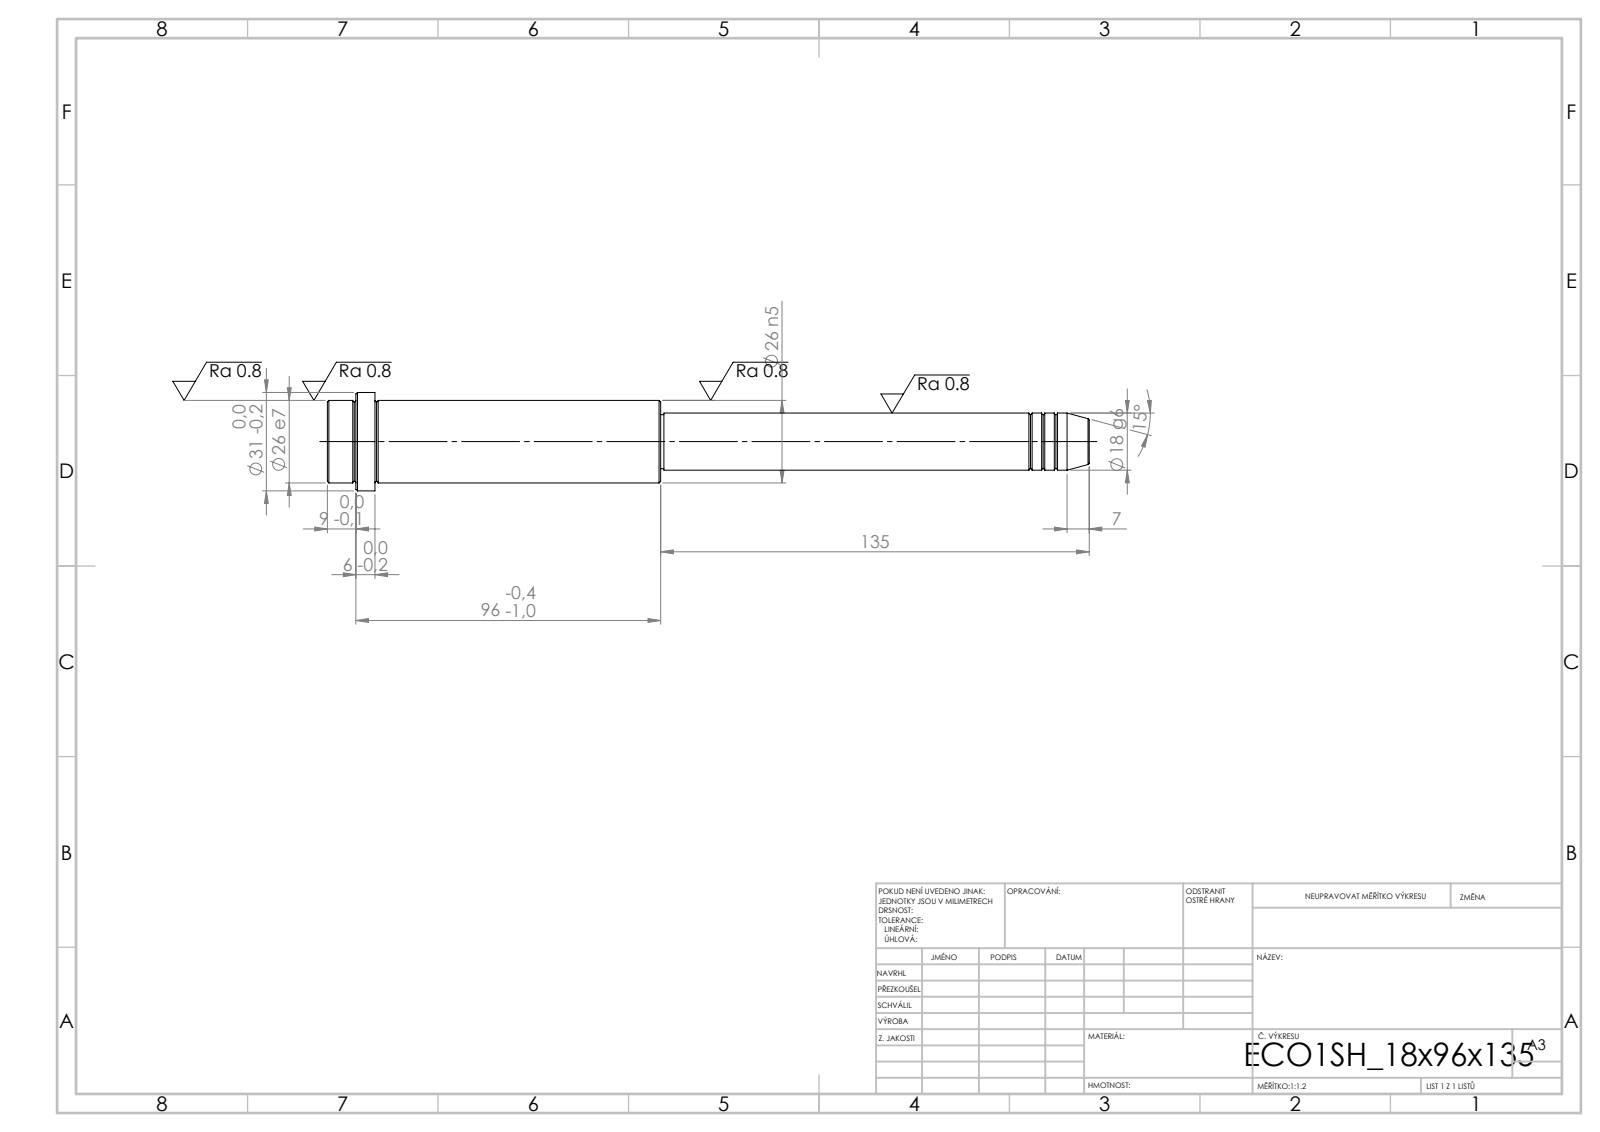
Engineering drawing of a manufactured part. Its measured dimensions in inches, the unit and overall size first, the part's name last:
Units: inches
Overall size (bounding box): 9.449 × 1.22 × 1.22
Round bosses / shafts (diameter × count): ⌀1.22 ×1, ⌀1.024 ×1, ⌀0.709 ×1, ⌀0.669 ×1
Main face-to-face distances: 4.134, 3.543, 0.591, 3.78, 0.236, 0.354, 5.315, 8.858, 9.094, 9.449
Volume: 5.548 in³ · Surface area: 27.64 in²
Bodies: 1 solid, 52 faces (6 planar, 16 cylindrical, 30 other)
STEP written by: SolidWorks 2019 (CONFIG_CONTROL_DESIGN)
